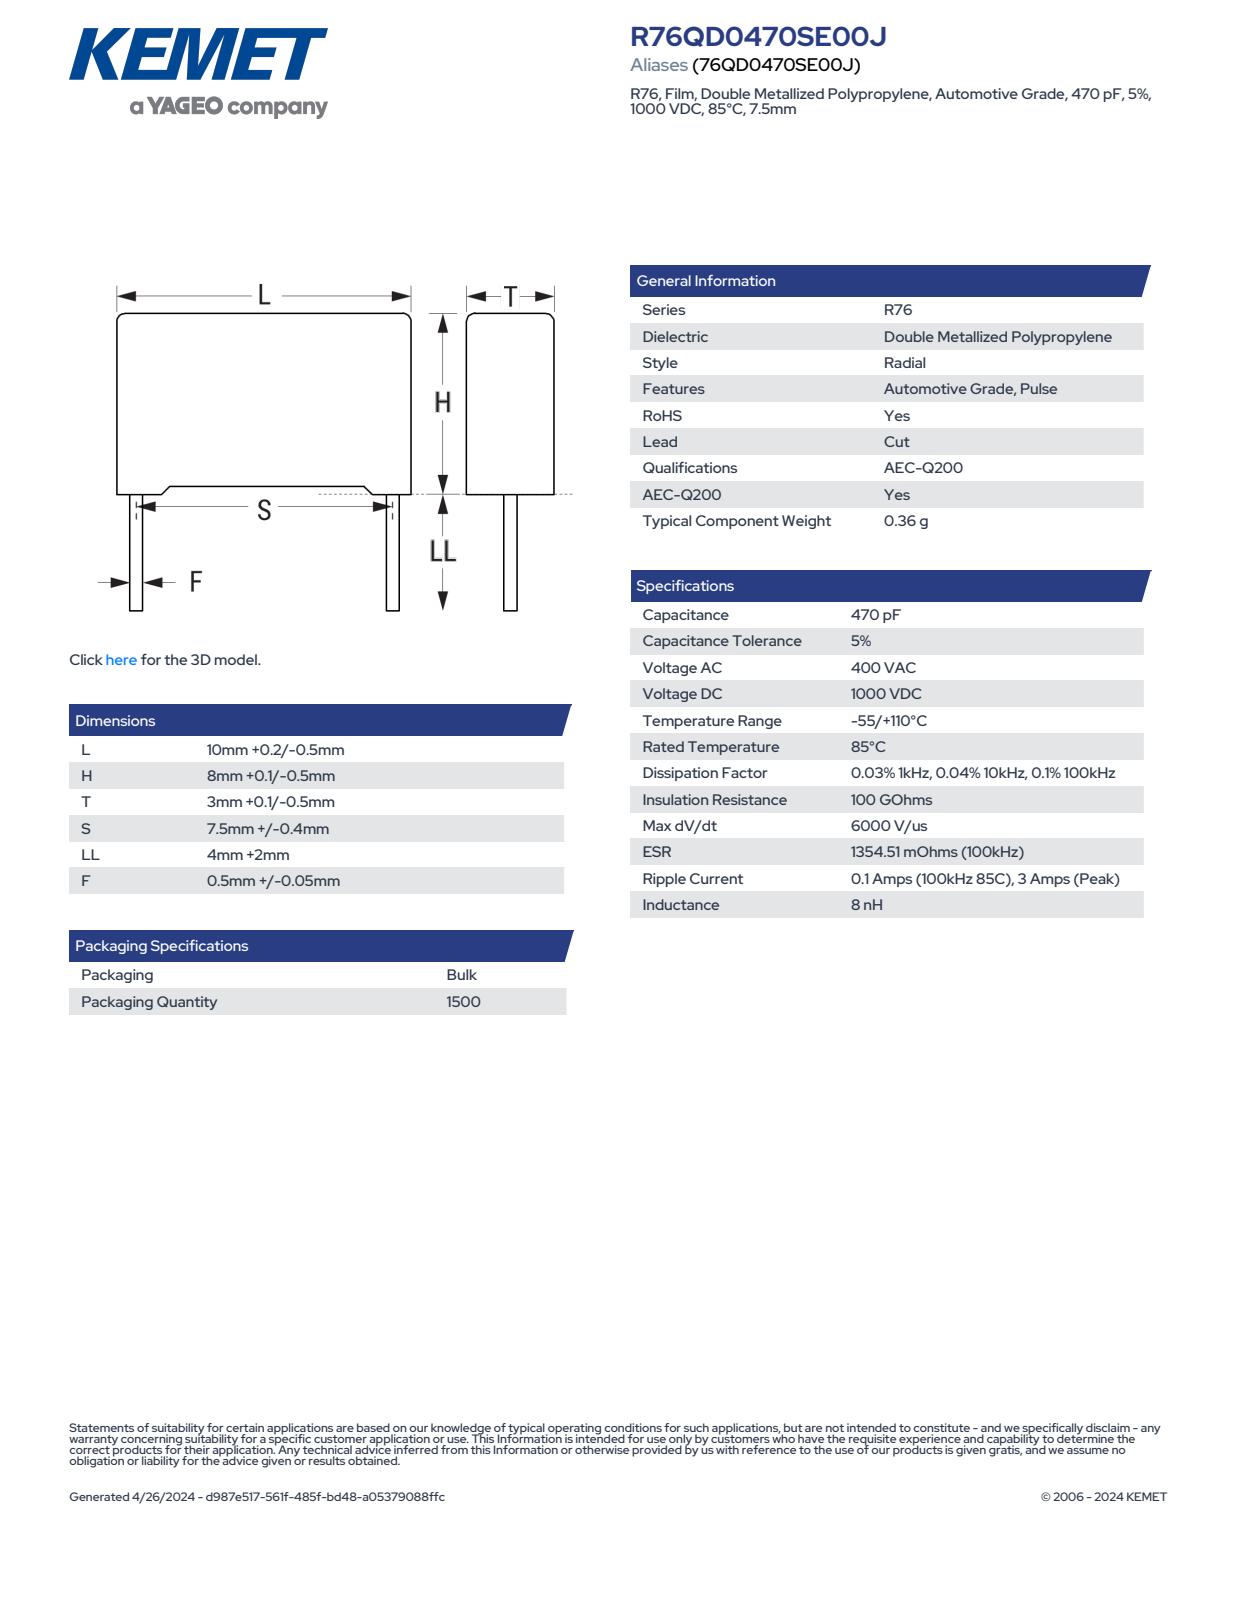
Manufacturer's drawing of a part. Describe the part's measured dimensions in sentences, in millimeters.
The part is named "CFR_RB2_10X8X3_L10.2H8.1T3.1S7.5LL6F0.55". Its 3-D file was written by "SolidWorks 2021 (AUTOMOTIVE_DESIGN)". It is 4 solids with 85 faces: 77 planar, 8 cylindrical and 0 other. Overall it measures 14.1 by 10.2 by 3.1 millimeters. Its volume is 240 cubic millimeters and its surface area 317 square millimeters. Round bosses or shafts: 2 of diameter 0.55. Partial cylindrical surfaces (rounded edges, fillets, slot ends): 4 of radius 0.5. The main face-to-face distances are 3.1, 10.2, 7.35, 0.34, 2.76, 2.42, 0.75, 8.1, 9.86, 0.47.
